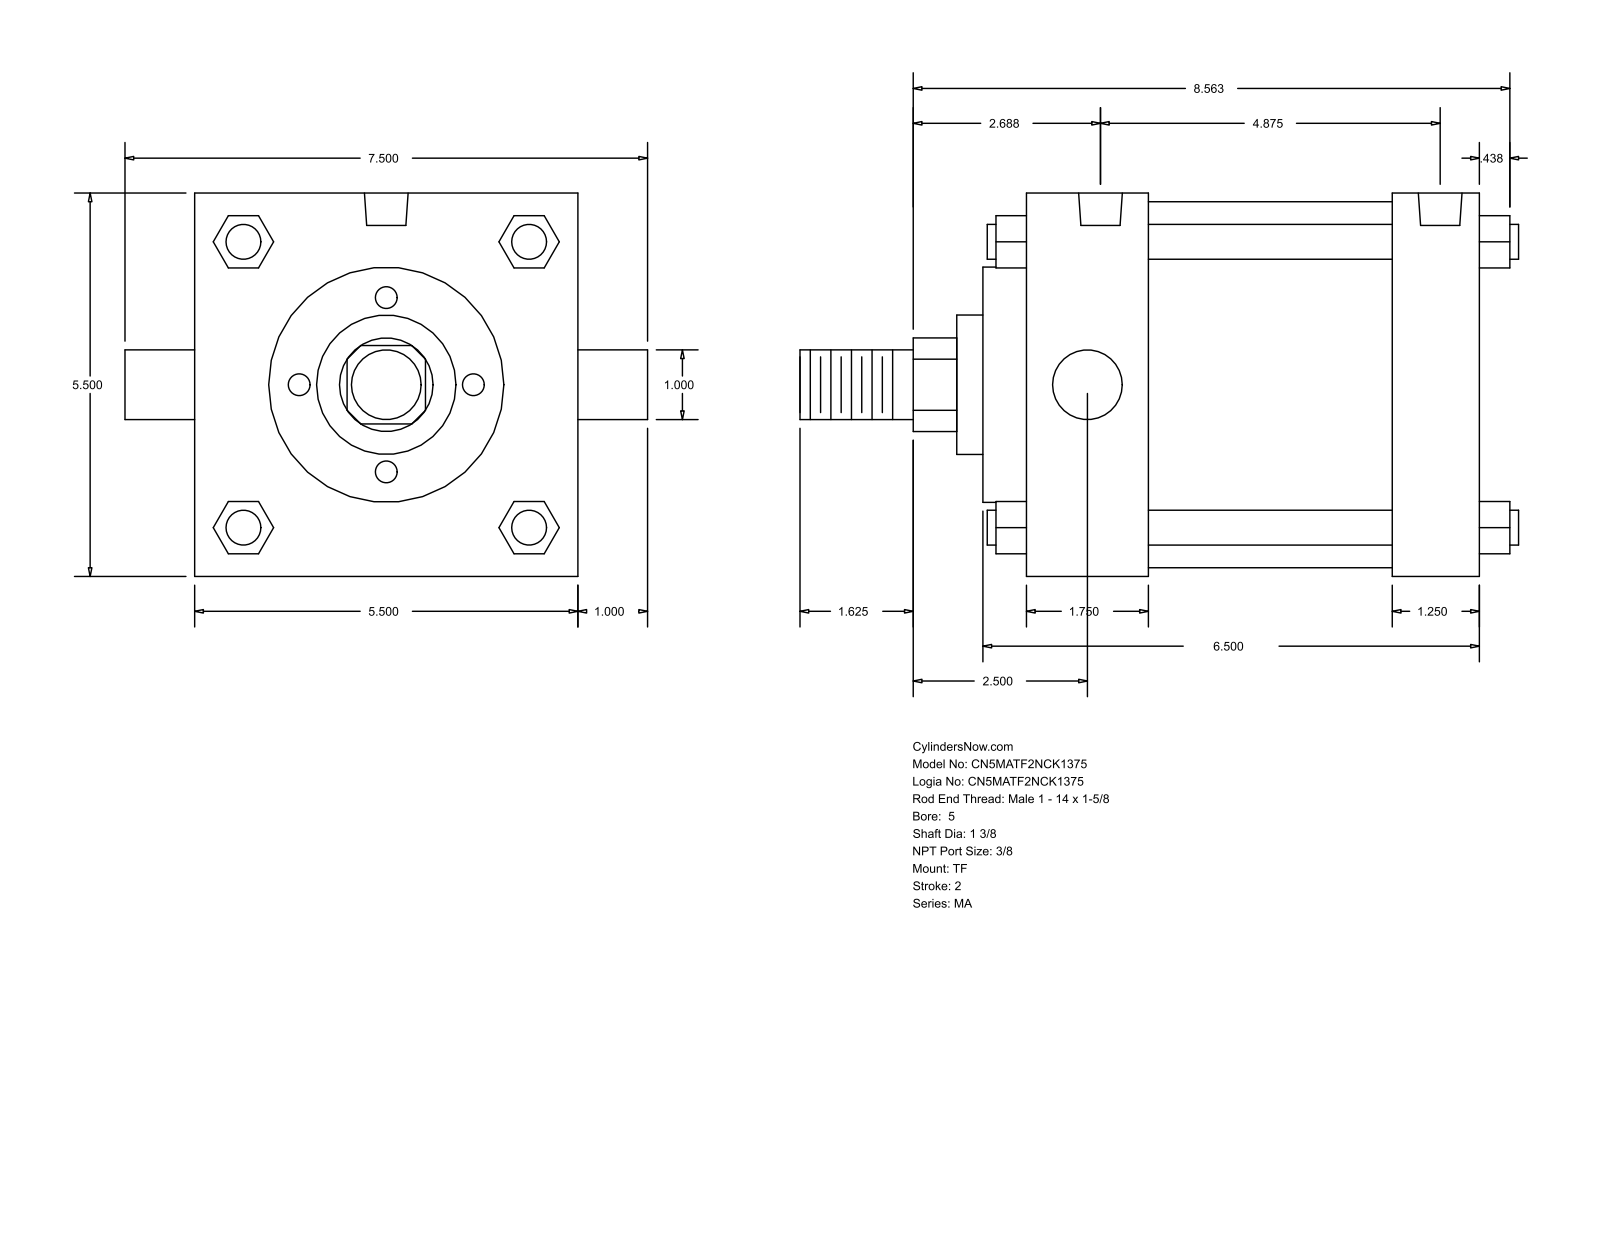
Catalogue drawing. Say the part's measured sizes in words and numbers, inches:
The part is named "MA_TF__0500_1.375". Its 3-D file was written by "GSSL Pune (CONFIG_CONTROL_DESIGN)". It is 0 solids with 122 faces: 93 planar, 29 cylindrical and 0 other. Overall it measures 10.313 by 7.5 by 5.5 inches. Round holes: 3 of diameter 0.437, 2 of diameter 0.627. Round bosses or shafts: 4 of diameter 0.5, 2 of diameter 1, 1 of diameter 5.25, 1 of diameter 3.375, 1 of diameter 2, 1 of diameter 1.375. Partial cylindrical surfaces (rounded edges, fillets, slot ends): 1 of radius 0.672. The main face-to-face distances are 5.5, 6.5, 5.25, 1.25, 1.75, 3.5, 4.75, 0.625, 2.375, 5.875. The hole center spacings are 0.188, 4.687, 4.5, 4.875.
